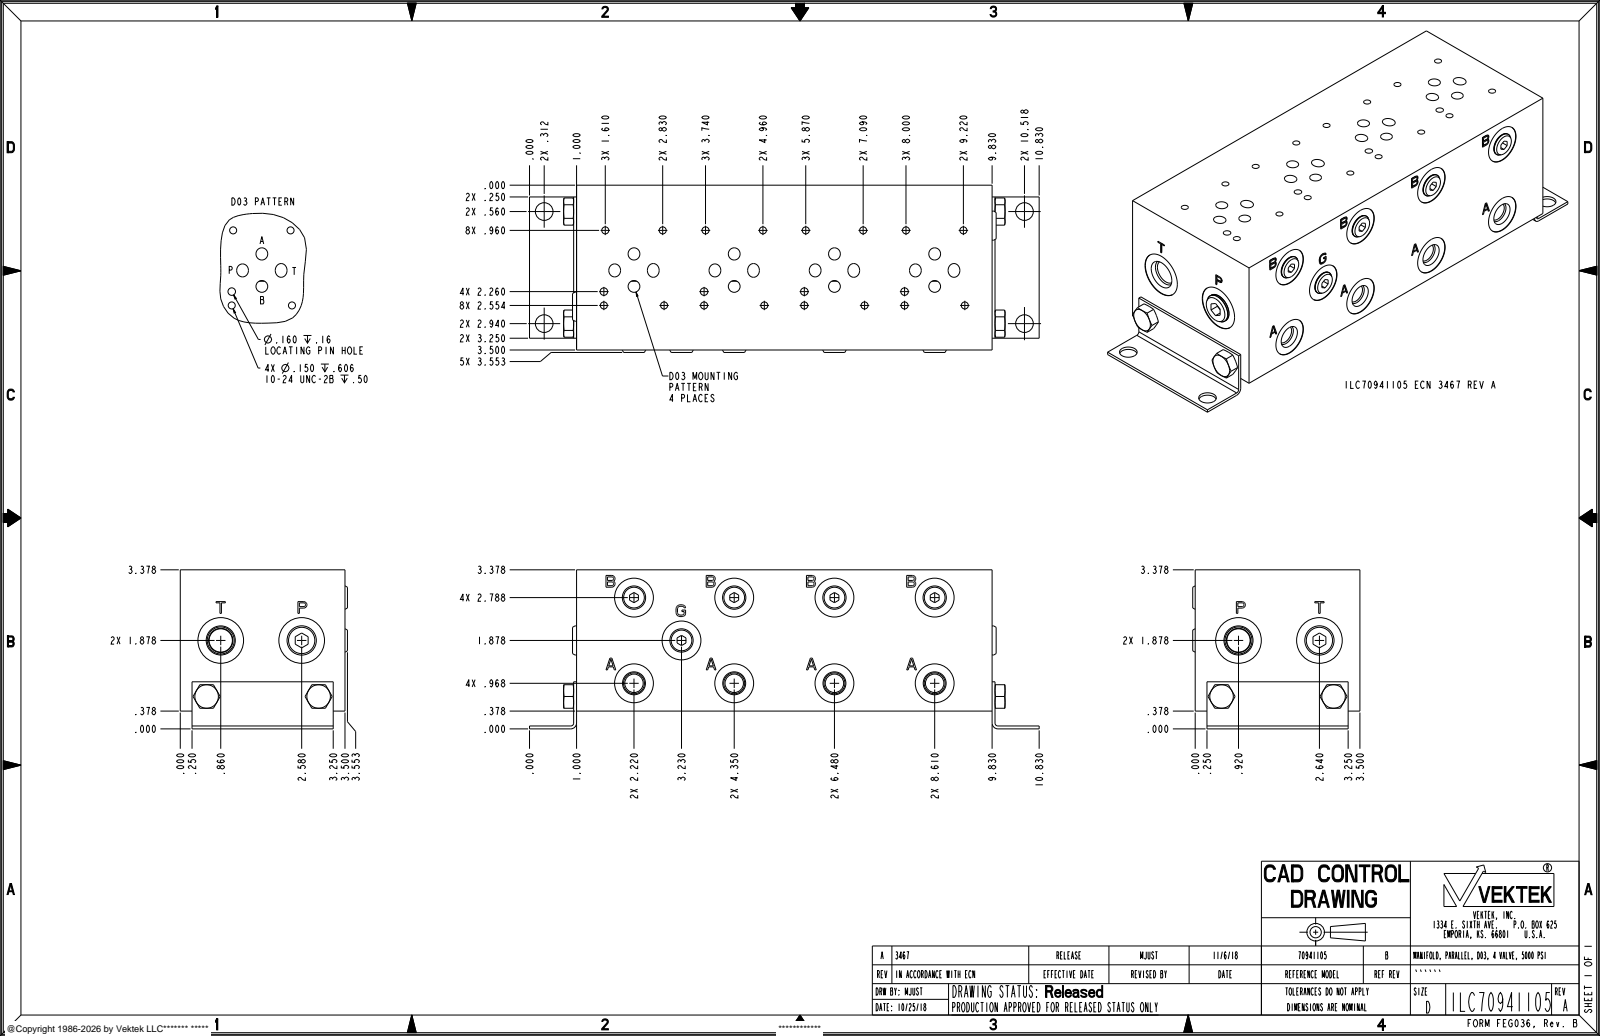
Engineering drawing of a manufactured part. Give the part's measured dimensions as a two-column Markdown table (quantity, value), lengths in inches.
| quantity | value |
| --- | --- |
| part name | ILC70941105 |
| STEP written by | PRO/ENGINEER BY PARAMETRIC TECHNOLOGY CORPORATION, 2013320 (AUTOMOTIVE_DESIGN) |
| units | inches |
| bodies | 1 solid, 811 faces (471 planar, 144 cylindrical, 196 other) |
| overall size | 10.83 × 3.553 × 3.378 |
| volume | 87.31 in³ |
| surface area | 221 in² |
| round holes (diameter × count) | 0.15 × 16, 0.25 × 16, 0.392 × 9, 0.825 × 9, 0.375 × 6, 0.16 × 4, 0.515 × 2, 0.97 × 2 |
| round bosses / shafts (diameter × count) | 0.48 × 2, 0.31 × 2 |
| partial cylindrical surfaces (radius × count) | 0.06 × 2, 0.125 × 2 |
| main face-to-face distances | 3, 3.5, 8.83, 0.062, 0.316, 3.316, 0.378, 3.378, 3.49, 0.062 |
| hole center spacings | 2.13, 4.26, 4.26, 1.337, 1.594, 2.026, 2.13, 6.39 |
